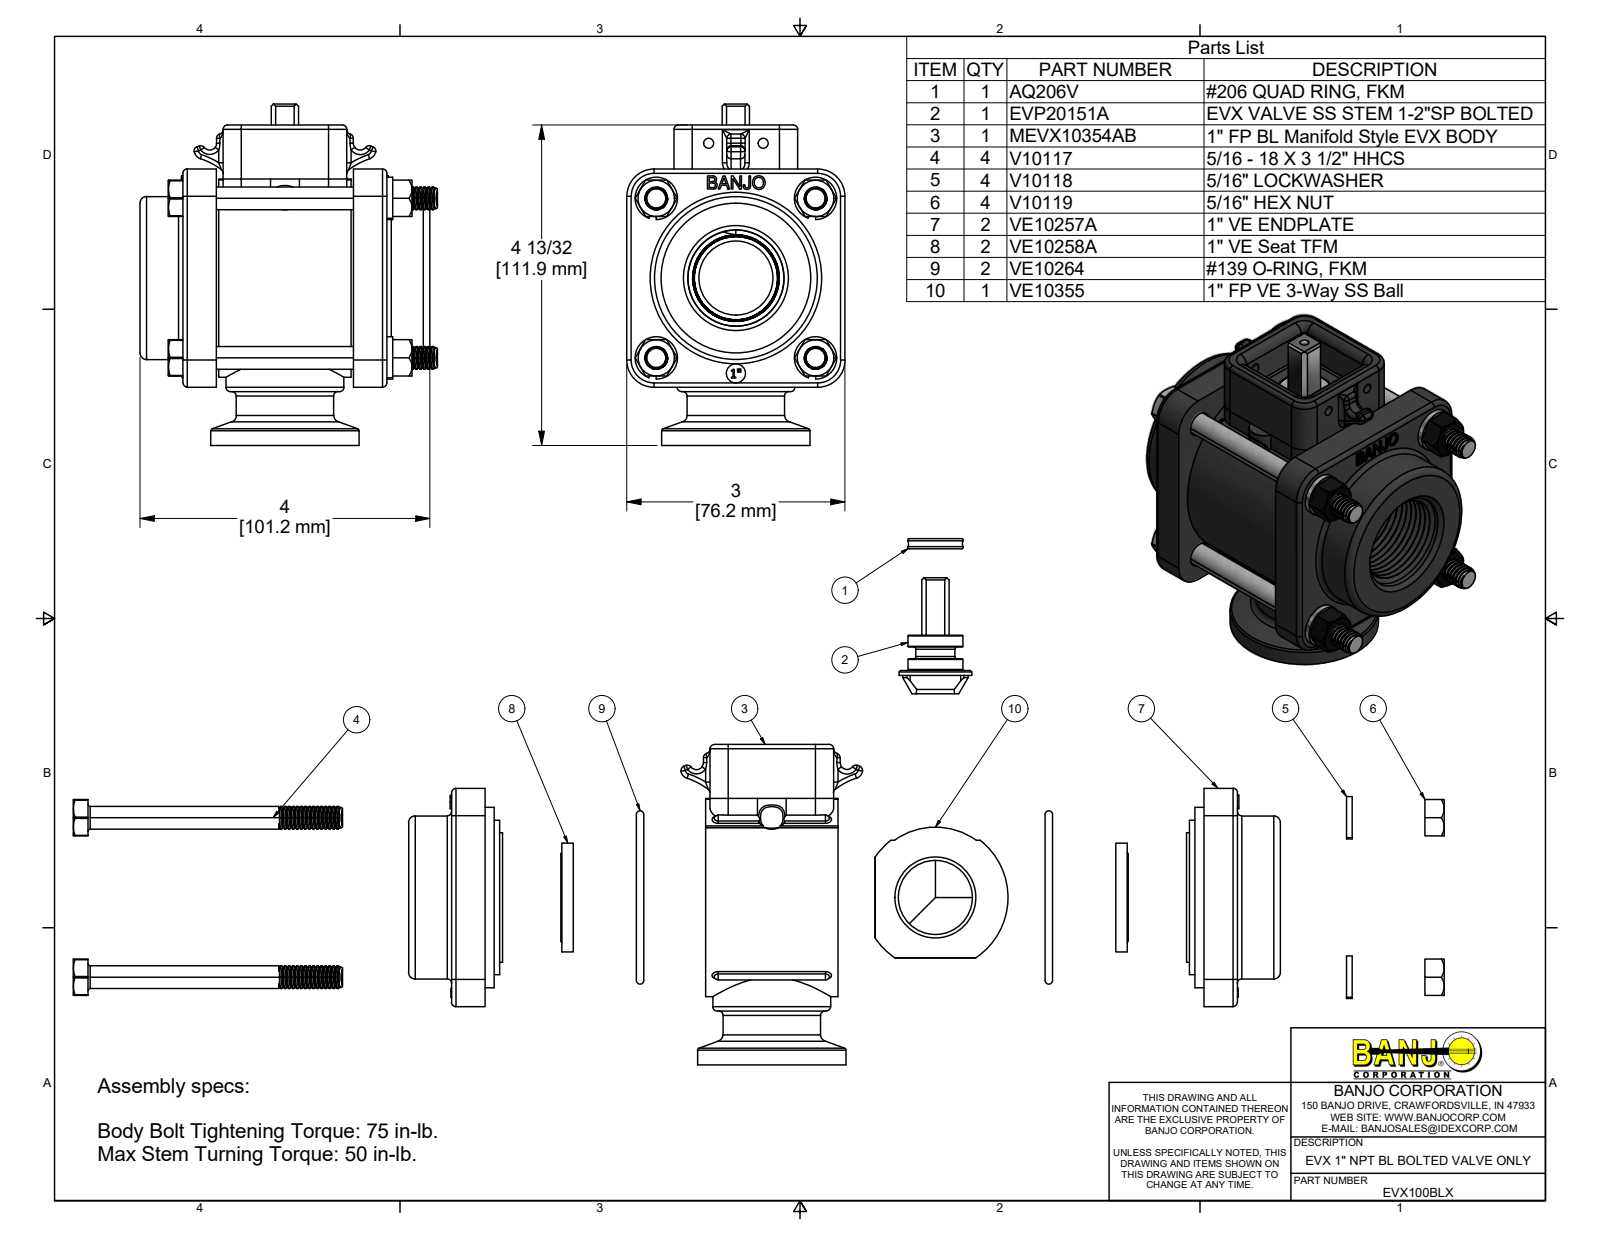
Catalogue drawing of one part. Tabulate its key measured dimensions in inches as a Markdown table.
| quantity | value |
| --- | --- |
| part name | EVX100BLX; MEVX10354AB; MEVX10354ABX; VE10355 (+8 more) |
| STEP written by | Autodesk Inventor 2019 (AUTOMOTIVE_DESIGN) |
| units | inches |
| bodies | 22 solids, 1547 faces (362 planar, 532 cylindrical, 653 other) |
| overall size | 38.771 × 4.693 × 3 |
| volume | 21.36 in³ |
| surface area | 351.2 in² |
| round holes (diameter × count) | 0.252 × 4, 0.322 × 4, 0.35 × 4, 1.02 × 3, 0.135 × 2, 0.26 × 1, 0.76 × 1, 1.38 × 1, 1.5 × 1, 2.12 × 1, 2.375 × 1, 2.5 × 1 |
| round bosses / shafts (diameter × count) | 0.268 × 60, 0.583 × 4, 0.313 × 4, 2.725 × 1, 2.48 × 1, 2.24 × 1, 2.124 × 1, 2.04 × 1 |
| partial cylindrical surfaces (radius × count) | 0.06 × 58, 0.03 × 12, 0.134 × 8, 0.375 × 8, 0.125 × 6, 0.21 × 4, 0.25 × 4, 0.284 × 4 |
| main face-to-face distances | 0.46, 2.345, 2.805, 1.885, 3, 0.125, 0.59, 1.05, 2.935, 3.395 |
| hole center spacings | 1.55, 2.192, 1.046, 1.117, 1.891, 2.644, 3.1, 3.186 |
